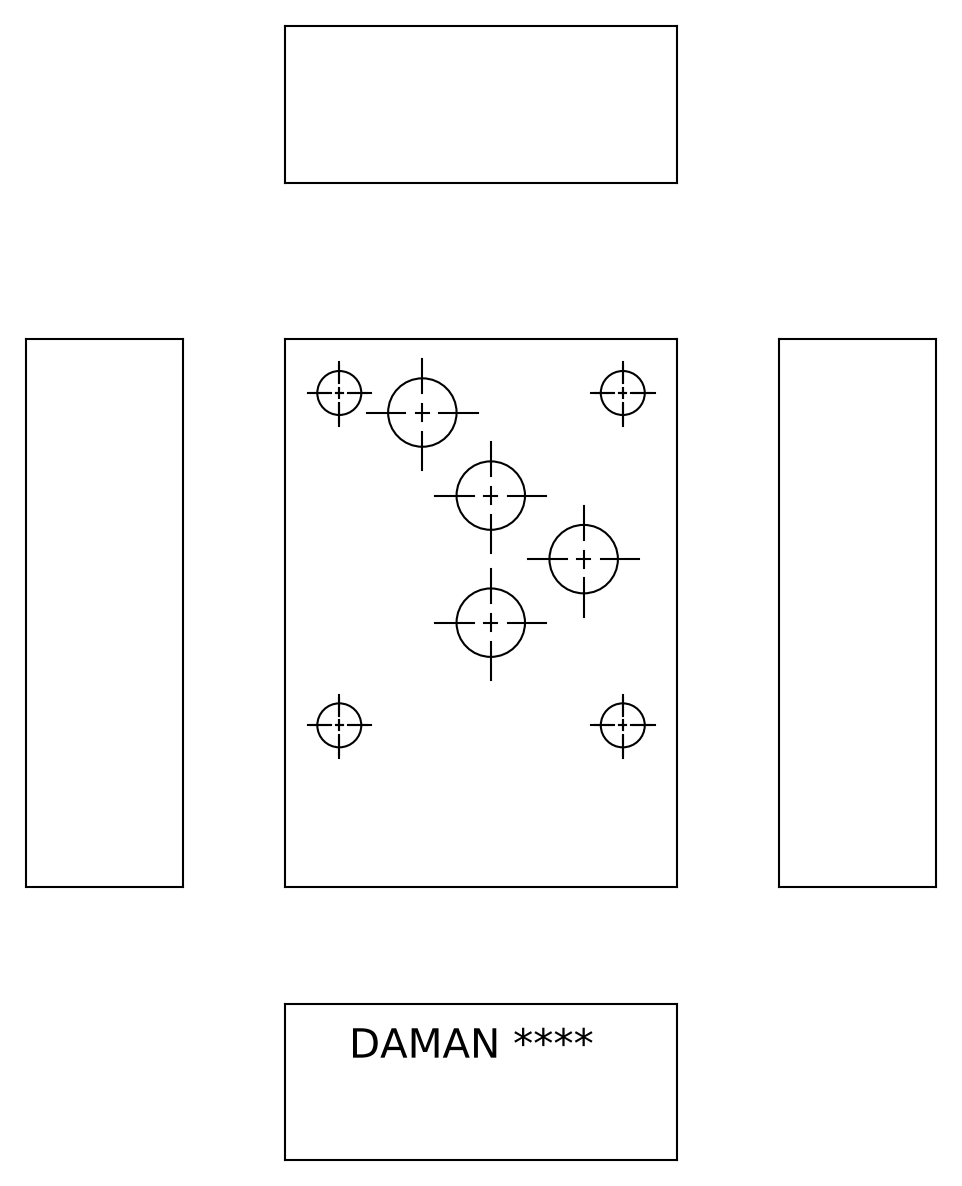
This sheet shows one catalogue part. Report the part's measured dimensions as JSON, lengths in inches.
{"part_name": "Part_DD05D1D04VAAB.B01731R3_3D", "step_written_by": "Autodesk Inventor 2019 (AUTOMOTIVE_DESIGN)", "units": "inches", "bodies": {"solids": 1, "faces": 398, "planar": 274, "cylindrical": 23, "other": 101}, "overall_size": [3.5, 2.5, 1], "volume_in3": 8.469, "surface_area_in2": 32.63, "round_holes": [[0.281, 7], [0.562, 6], [0.375, 5], [0.437, 2], [0.438, 2]], "face_to_face_distances": [1, 2.5, 3.5, 0.96, 0.04, 3.461, 0.039, 0.143, 0.149, 0.308], "hole_center_spacings": [1.091, 1.811, 2.126, 0.659, 1.117, 1.117, 1.118, 1.673]}
